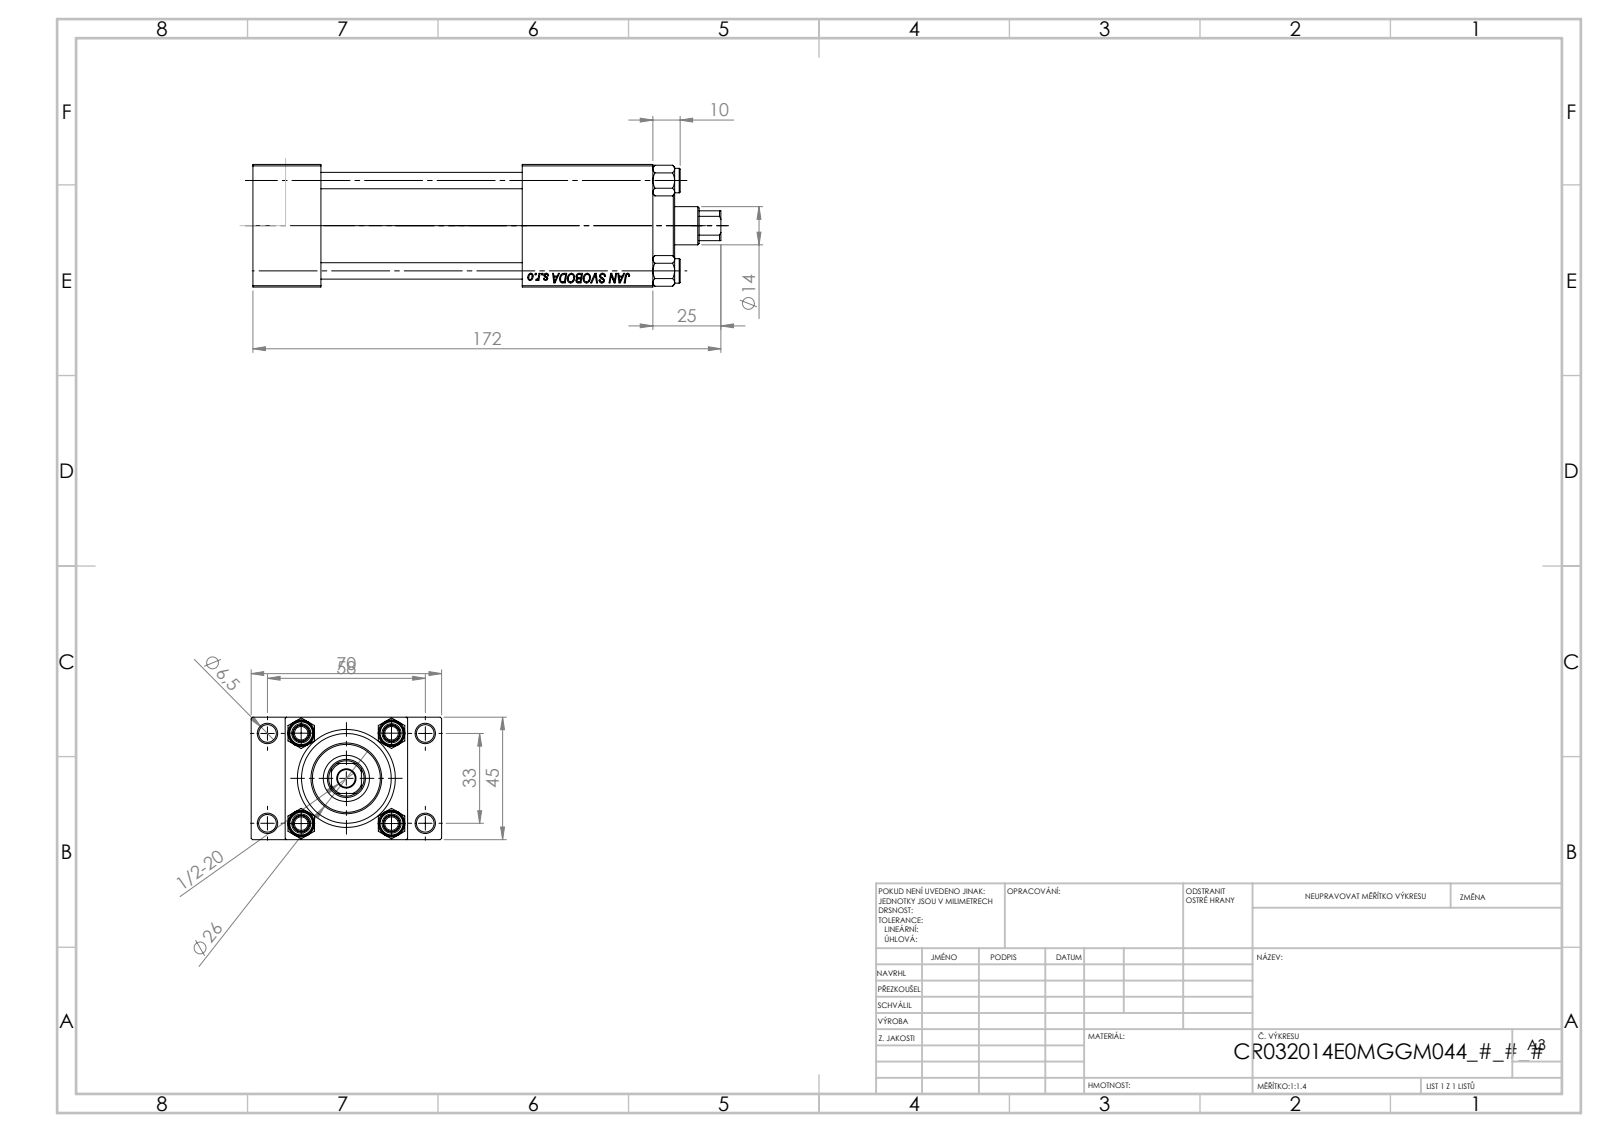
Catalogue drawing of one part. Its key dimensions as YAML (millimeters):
part_name: "V215CR_E_Body; V215_VC_A; NUT_M5_E; V215CR_TYCINKA_E (+1 more)"
step_written_by: "SolidWorks 2019 (CONFIG_CONTROL_DESIGN)"
units: millimeters
bodies: {solids: 11, faces: 1136, planar: 497, cylindrical: 87, other: 552}
overall_size: [172, 70, 45]
volume: 234399
surface_area: 84216
round_holes:
  - {diameter: 6.5, count: 5}
  - {diameter: 6, count: 4}
  - {diameter: 7, count: 2}
  - {diameter: 13.16, count: 2}
  - {diameter: 20, count: 2}
  - {diameter: 14, count: 1}
  - {diameter: 17, count: 1}
  - {diameter: 24, count: 1}
  - {diameter: 32, count: 1}
  - {diameter: 33, count: 1}
round_bosses_or_shafts:
  - {diameter: 9, count: 4}
  - {diameter: 38, count: 1}
  - {diameter: 26, count: 1}
partial_cylinders:
  - {radius: 6.5, count: 1}
face_to_face_distances: [45, 25, 12.5, 57.5, 147, 122, 70, 99, 74, 48]
hole_center_spacings: [12.4, 23.48, 33.2, 33.37, 35.35, 45.6, 56.35, 33]
